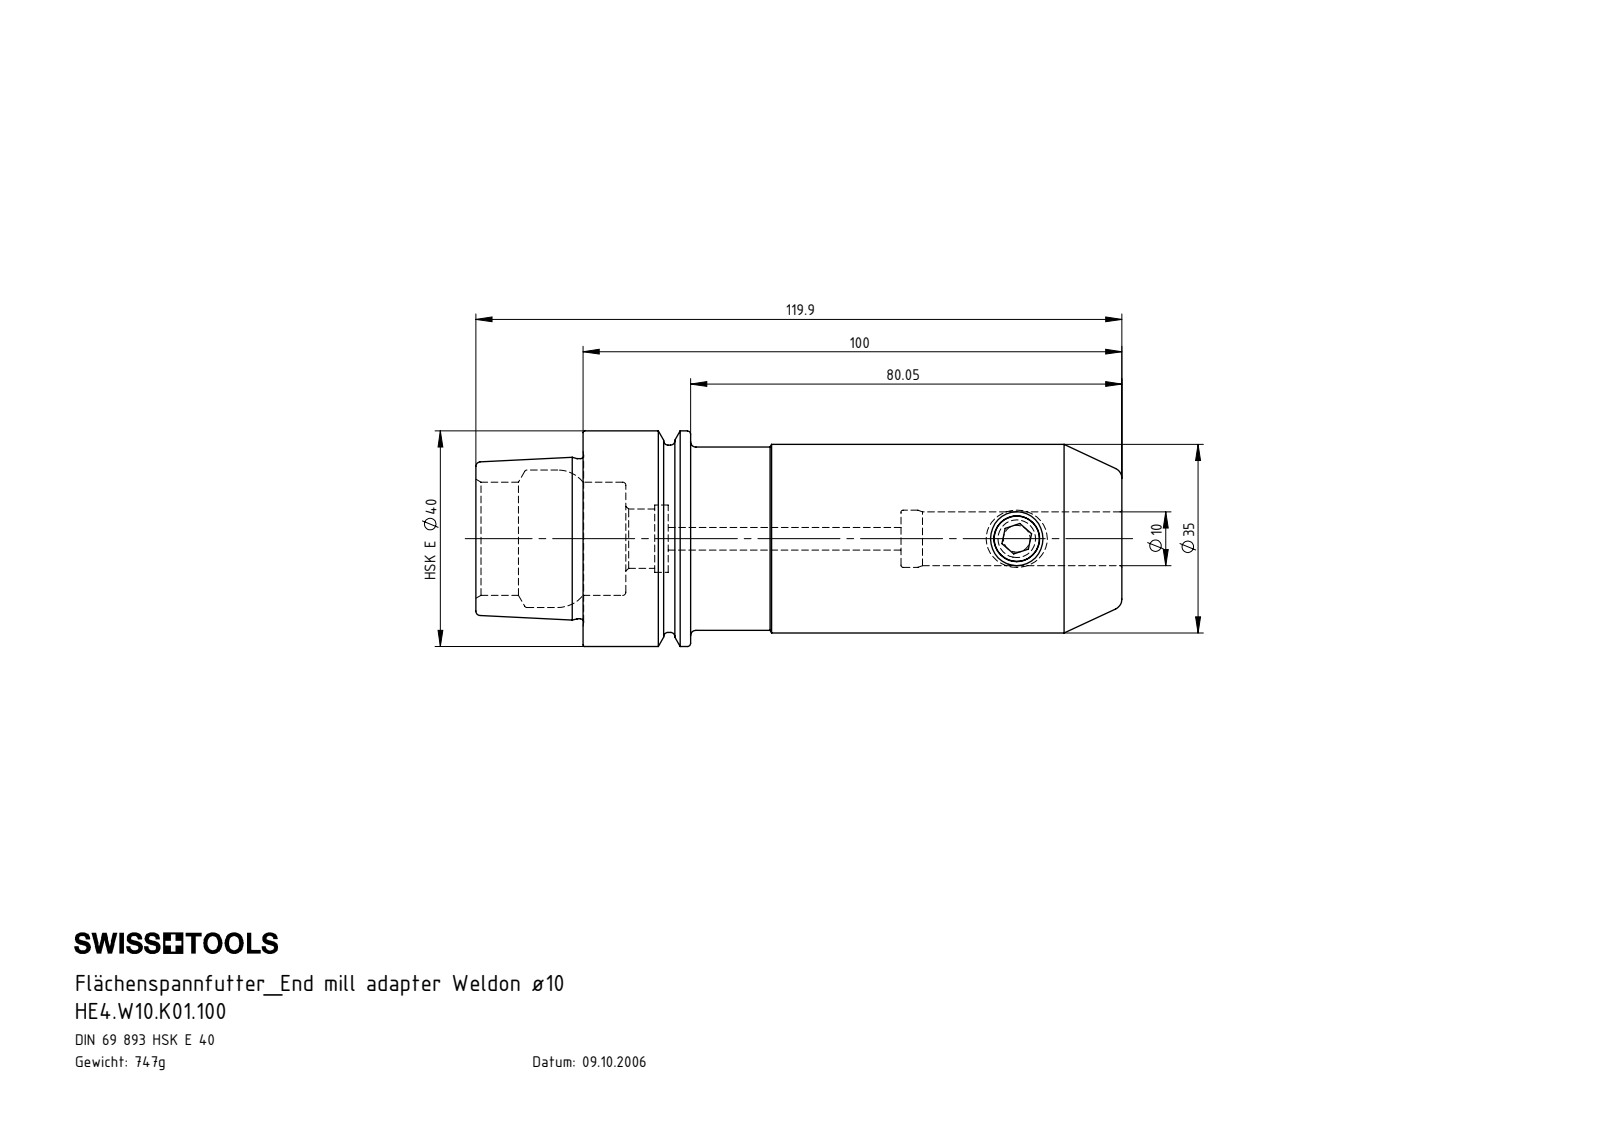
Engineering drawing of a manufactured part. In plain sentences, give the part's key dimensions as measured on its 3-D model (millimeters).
The part is named "HE4.W10.K01.100; W10-ER1.001.012; HE4-W10.K01.100_B_Fertigbearbeitung". Its 3-D file was written by "SolidWorks 2012 (AUTOMOTIVE_DESIGN)". It is 2 solids with 113 faces: 19 planar, 32 cylindrical and 62 other. Overall it measures 119.9 by 40 by 40 millimeters. Its volume is 95 148 cubic millimeters and its surface area 20 387 square millimeters. Round holes: 1 of diameter 4.2, 1 of diameter 8.5, 1 of diameter 10, 1 of diameter 10.6, 1 of diameter 11, 1 of diameter 12.5, 1 of diameter 21, 1 of diameter 25.5. Round bosses or shafts: 1 of diameter 40, 1 of diameter 35, 1 of diameter 34.75, 1 of diameter 34, 1 of diameter 29.71, 1 of diameter 10. The main face-to-face distances are 100, 7.95, 92.05, 19.9, 27.85, 119.9, 39.85, 19.95, 12, 80.05.
